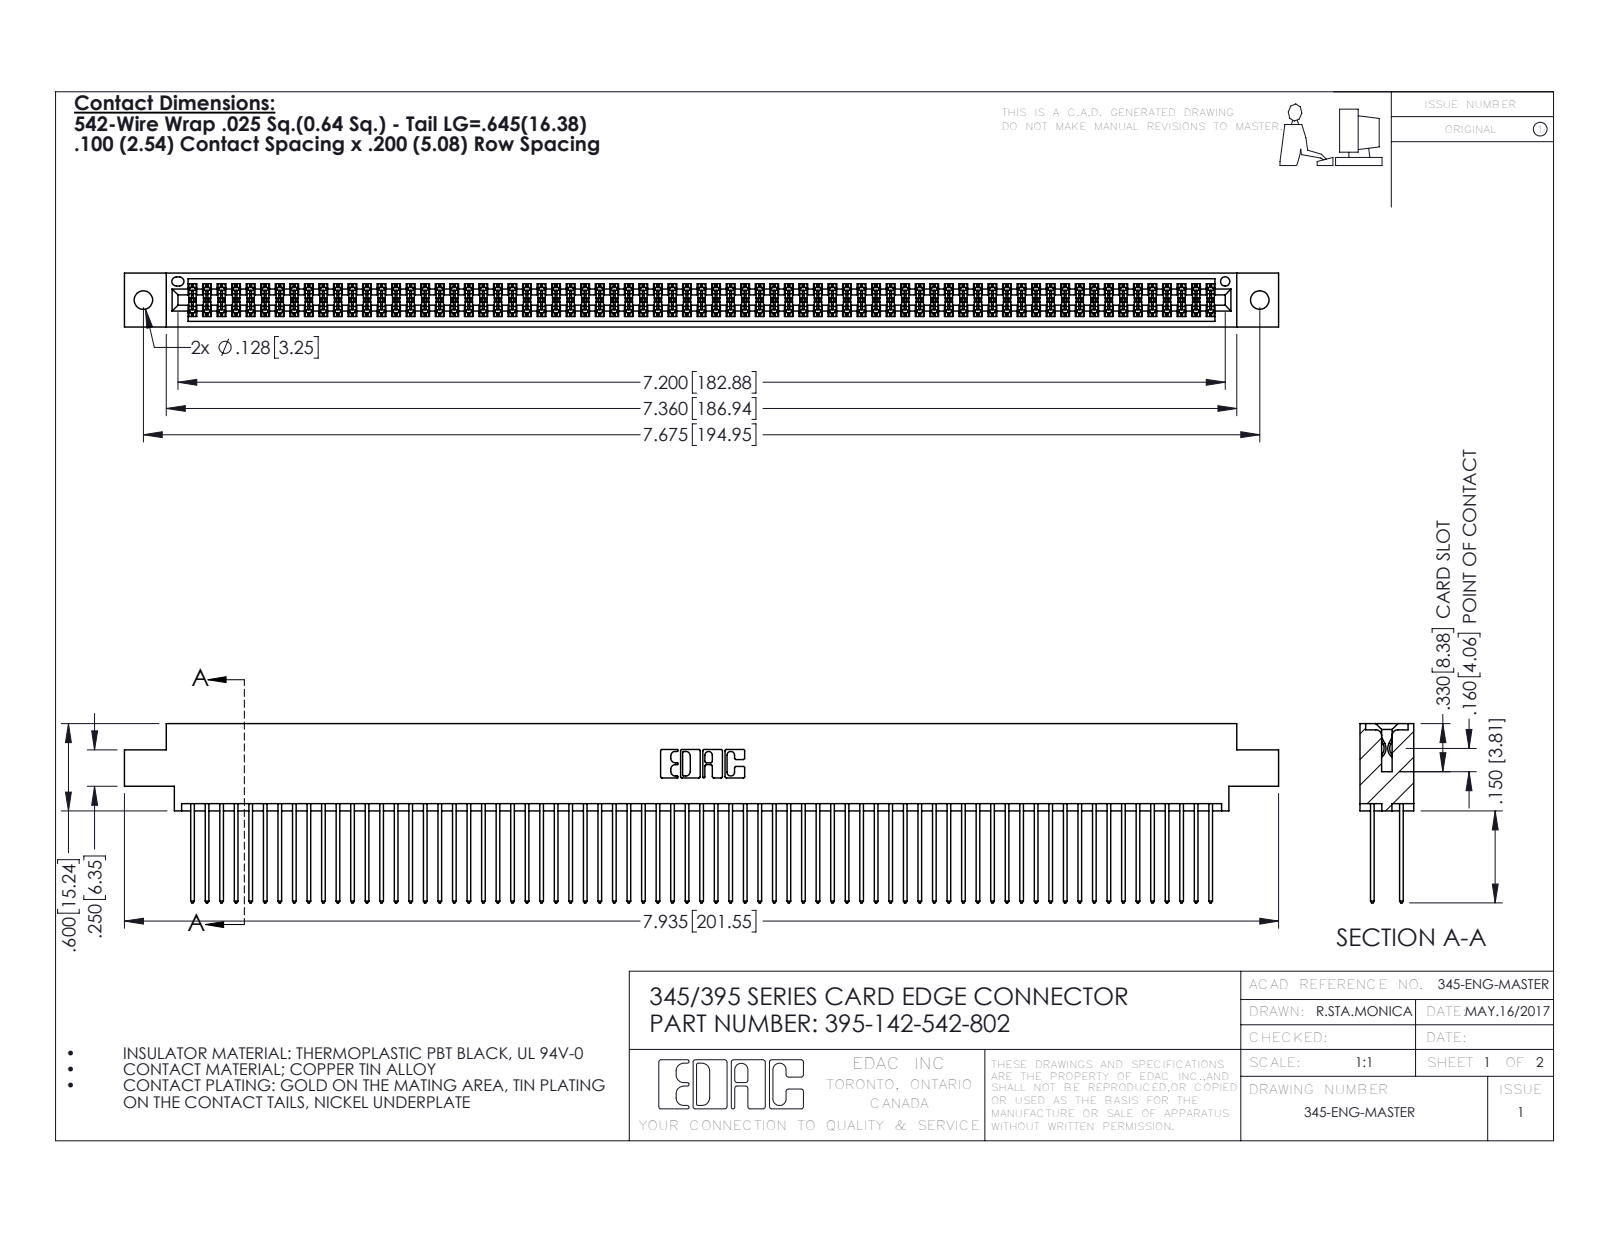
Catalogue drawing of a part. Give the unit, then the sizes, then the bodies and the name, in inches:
Units: inches
Overall size (bounding box): 7.935 × 1.232 × 0.37
Round holes (diameter × count): ⌀0.128 ×2, ⌀0.064 ×1
Partial cylindrical surfaces — rounded edges, fillets, slot ends (radius × count): R0.006 ×213, R0.01 ×142, R0.01 ×22, R0.007 ×6, R0.031 ×6, R0.026 ×3, R0.014 ×2, R0.019 ×2
Main face-to-face distances: 0.298, 0.072, 0.2, 0.098, 0.272, 0.025, 0.225, 0.37, 0.175, 0.149
Hole centre spacings: 0.27, 7.439, 7.675
Volume: 1.242 in³ · Surface area: 52.11 in²
Bodies: 143 solids, 7230 faces (4770 planar, 2460 cylindrical, 0 other)
Part name (STEP PRODUCT): 345-292-001_345-293-142; 345 Part_0.170 Offset - 0.128 Dia; 395-142-542-802
STEP written by: SolidWorks 2016 (CONFIG_CONTROL_DESIGN)
